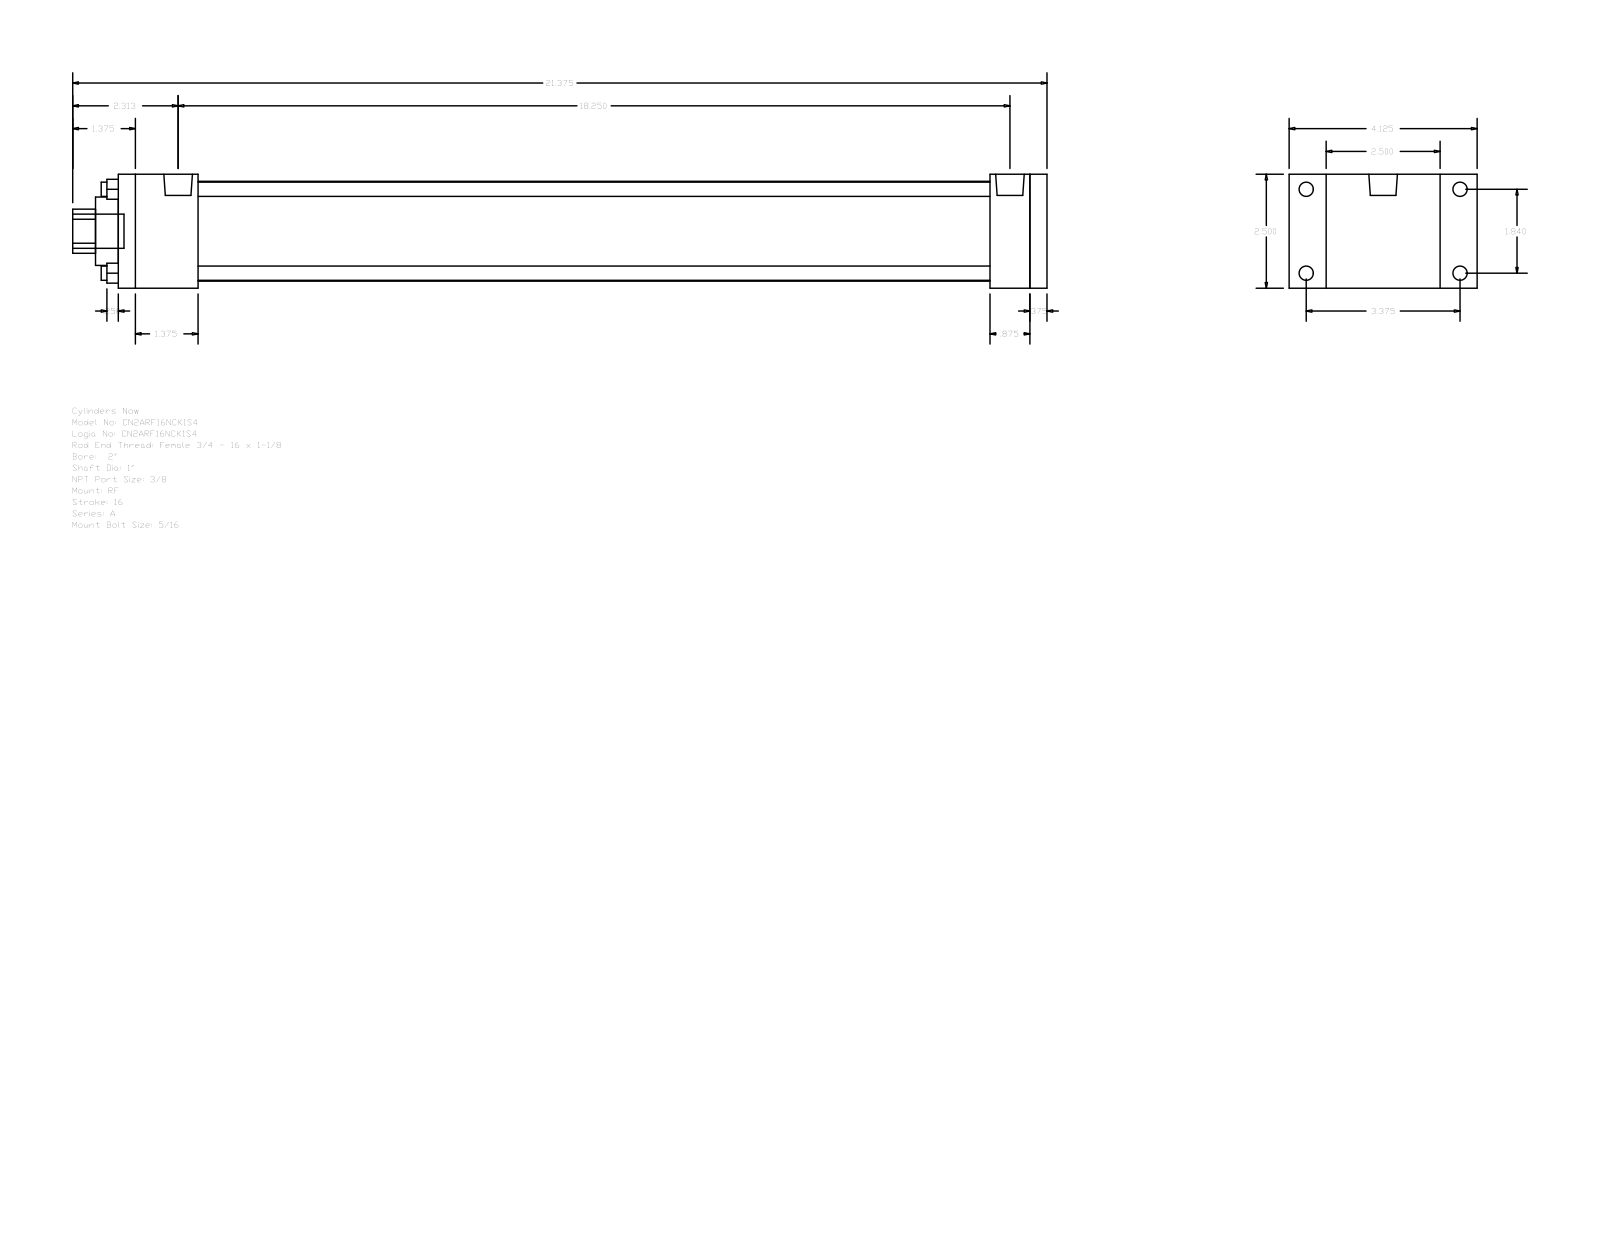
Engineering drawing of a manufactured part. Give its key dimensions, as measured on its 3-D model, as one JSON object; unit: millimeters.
{"part_name": "A_RF__0200_1", "step_written_by": "GSSL Pune (CONFIG_CONTROL_DESIGN)", "units": "millimeters", "bodies": {"solids": 0, "faces": 92, "planar": 64, "cylindrical": 28, "other": 0}, "overall_size": [542.92, 104.78, 63.5], "round_holes": [[7.94, 4], [25.4, 1], [38.1, 1], [55.63, 1]], "round_bosses_or_shafts": [[7.94, 4], [5.56, 4], [15.93, 2], [19.05, 1]], "partial_cylinders_radius": [[12.29, 1]], "face_to_face_distances": [63.5, 9.52, 517.52, 508, 20.64, 44.45, 463.55, 473.07, 485.78, 441.33], "hole_center_spacings": [33.05, 46.74, 66.1]}
